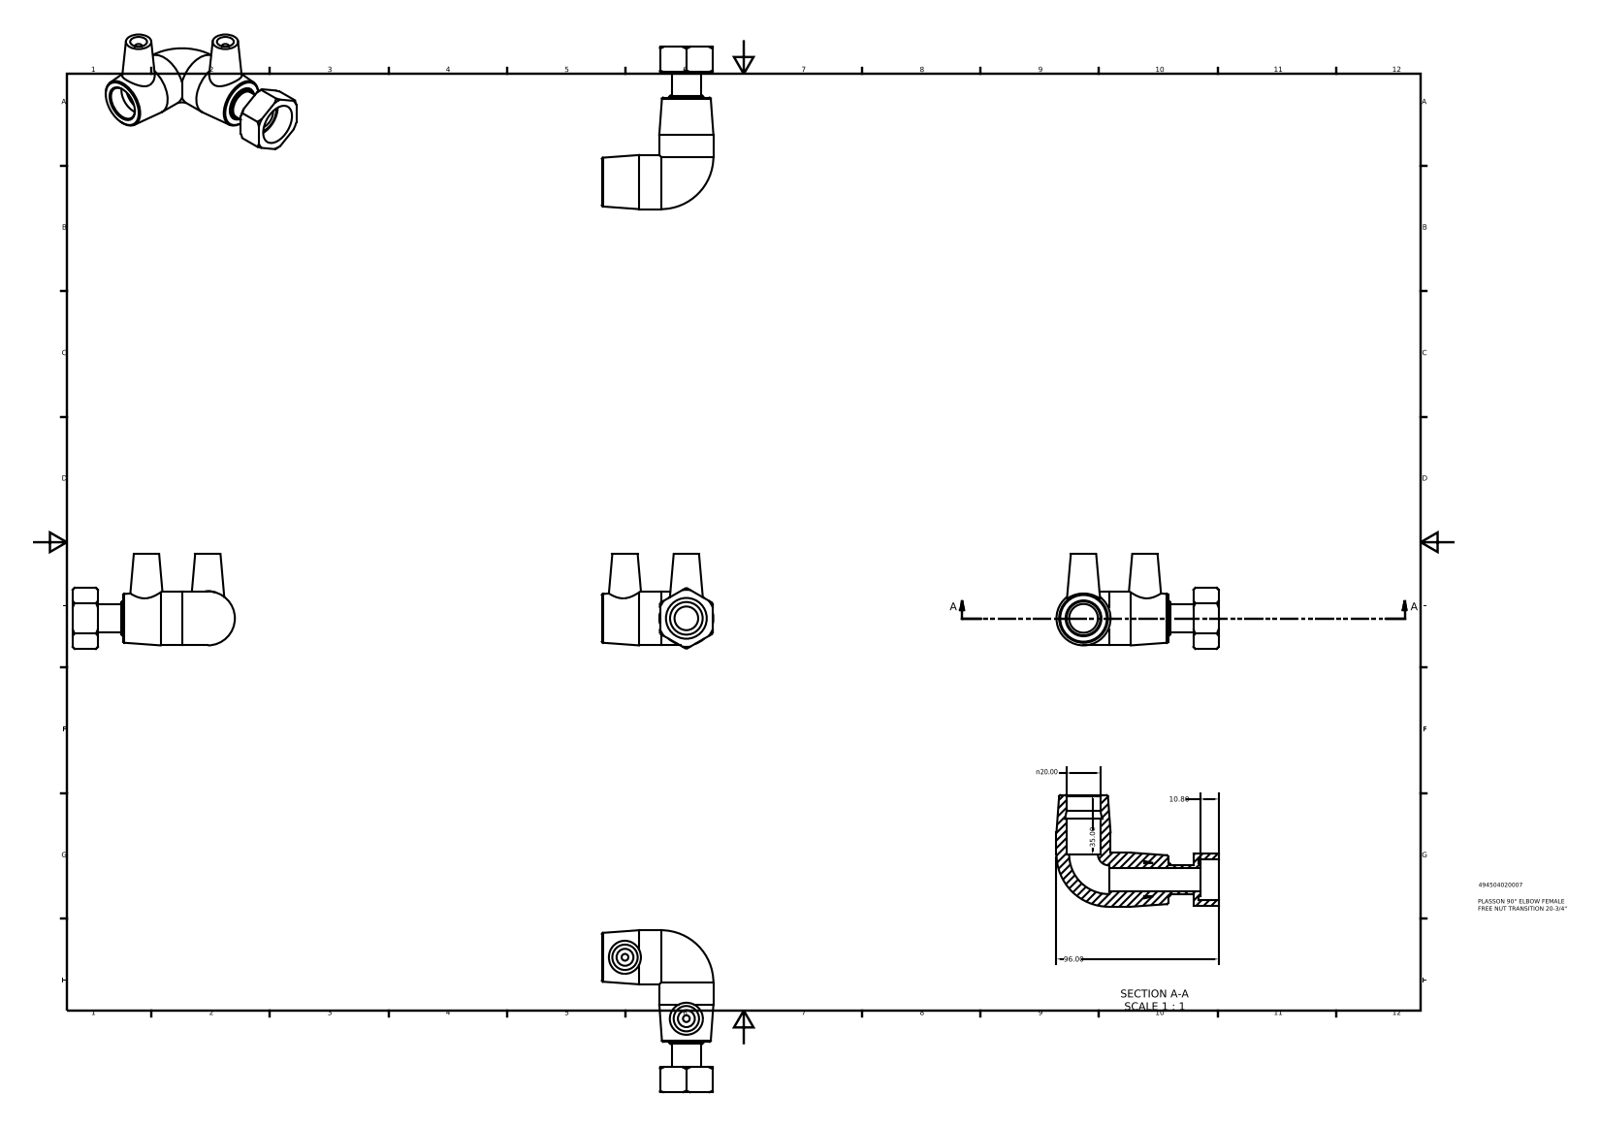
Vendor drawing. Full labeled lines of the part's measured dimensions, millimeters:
Part name (STEP PRODUCT): 494504020007
STEP written by: Autodesk Inventor 2015 (AUTOMOTIVE_DESIGN)
Units: millimetres
Bodies: 1 solid, 63 faces (23 planar, 14 cylindrical, 26 other)
Overall size (bounding box): 96 × 66 × 56.09
Volume: 67 221 mm³ · Surface area: 24 877 mm²
Round holes (diameter × count): ⌀10 ×2, ⌀14 ×1, ⌀20 ×1, ⌀24.12 ×1
Round bosses / shafts (diameter × count): ⌀32 ×2, ⌀4 ×2, ⌀20 ×1, ⌀19.29 ×1, ⌀16.88 ×1
Main face-to-face distances: 31.32, 15, 30, 14, 34.34, 65.66, 18, 1.2, 3, 12
Hole centre spacings: 51.34
